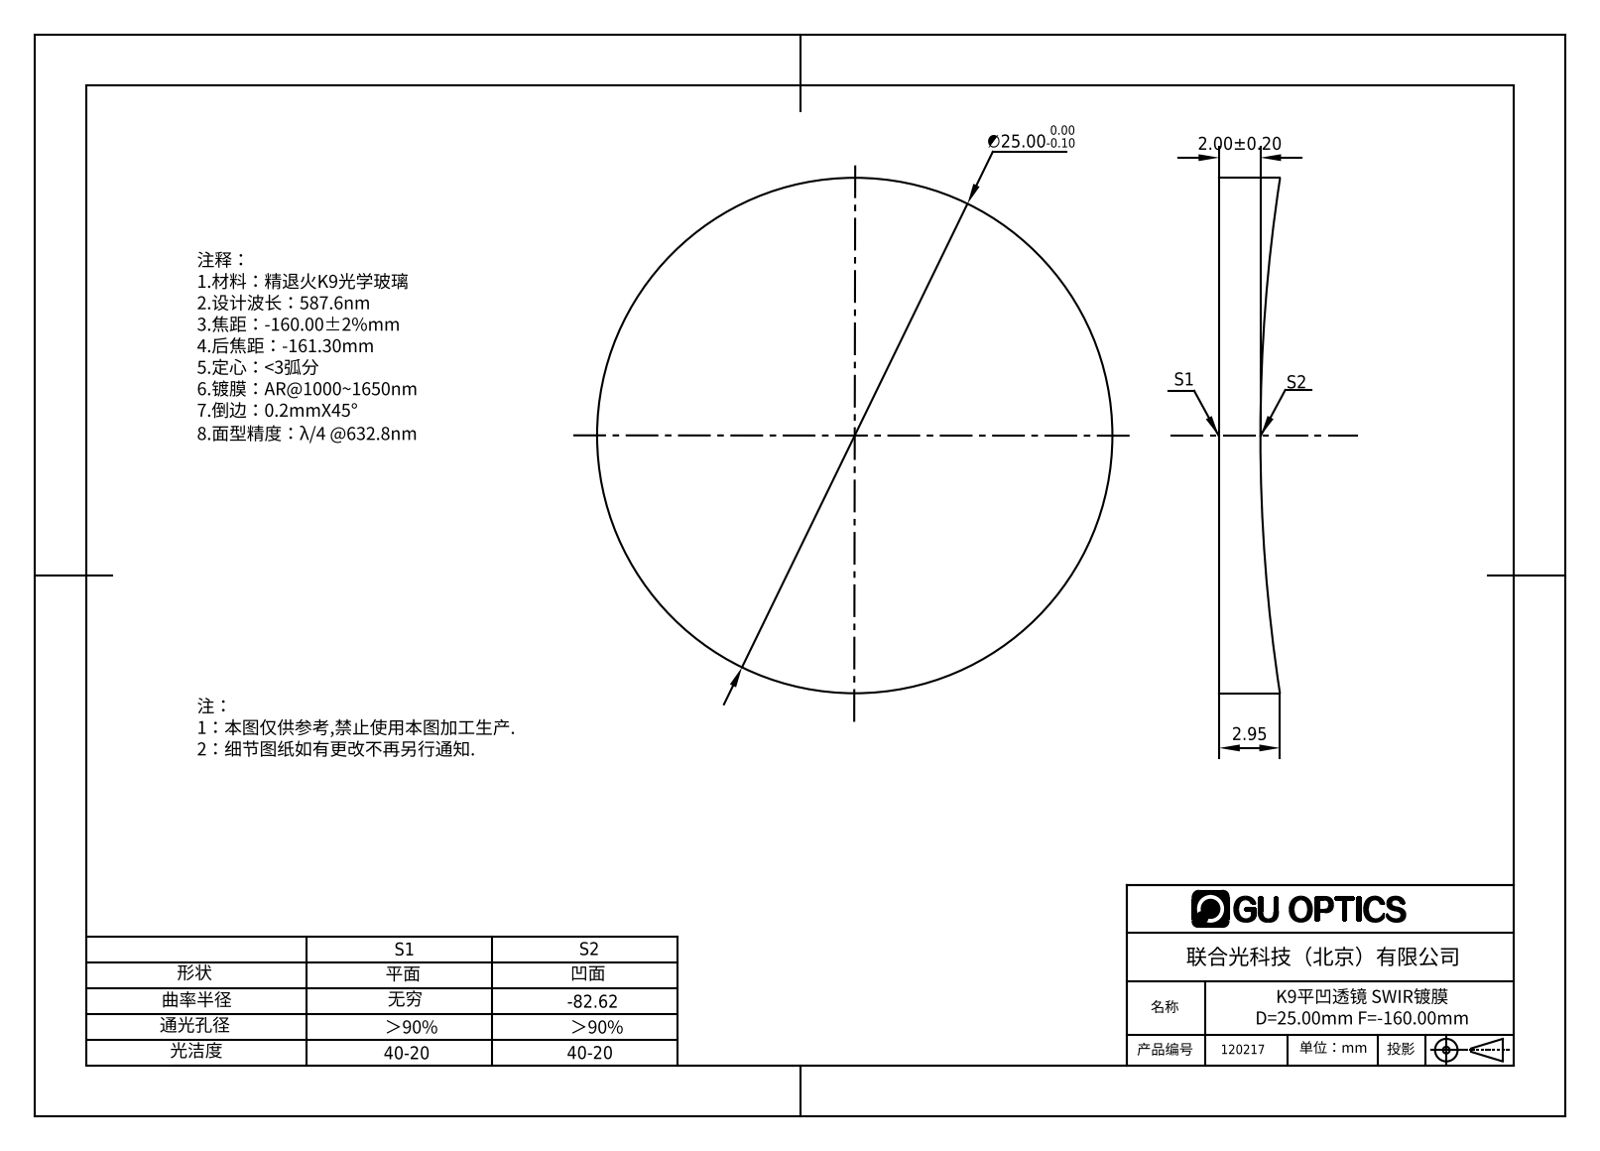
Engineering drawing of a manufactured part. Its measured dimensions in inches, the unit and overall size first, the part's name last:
Units: inches
Overall size (bounding box): 0.984 × 0.984 × 0.116
Round bosses / shafts (diameter × count): ⌀0.984 ×1
Volume: 0.074 in³ · Surface area: 1.886 in²
Bodies: 1 solid, 5 faces (1 planar, 2 cylindrical, 2 other)
Part name (STEP PRODUCT): 120157
STEP written by: SolidWorks 2016 (AUTOMOTIVE_DESIGN)
